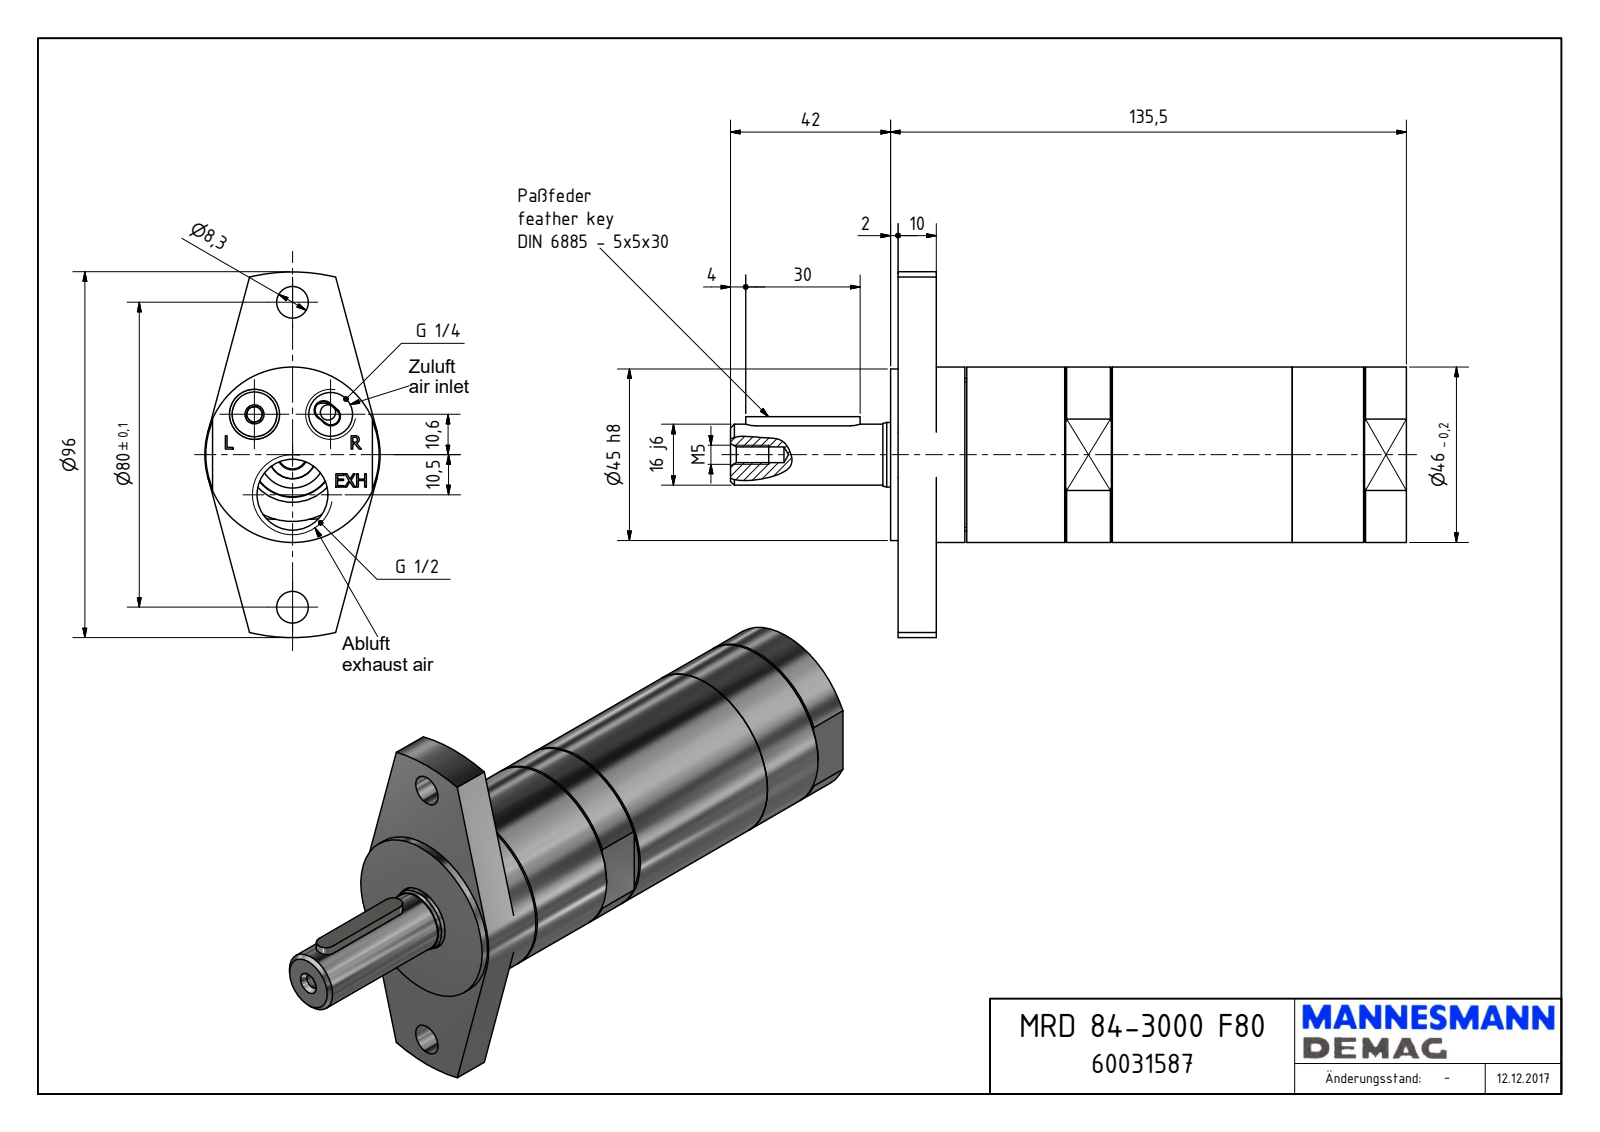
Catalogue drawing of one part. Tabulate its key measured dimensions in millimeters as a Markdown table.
| quantity | value |
| --- | --- |
| part name | MRD 84-3000 F80_60031587 |
| STEP written by | Autodesk Inventor 2018 (AUTOMOTIVE_DESIGN) |
| units | millimeters |
| bodies | 1 solid, 165 faces (108 planar, 31 cylindrical, 26 other) |
| overall size | 177.5 × 96 × 46 |
| volume | 243 723 mm³ |
| surface area | 32 705 mm² |
| round holes (diameter × count) | 8.3 × 2, 4 × 1, 4.13 × 1, 11.45 × 1, 17.5 × 1, 18.63 × 1 |
| round bosses / shafts (diameter × count) | 46 × 1, 45 × 1, 40 × 1, 33.34 × 1, 16.95 × 1, 16 × 1 |
| partial cylindrical surfaces (radius × count) | 2.5 × 2, 5 × 2, 5.72 × 1, 19 × 1, 48 × 1 |
| main face-to-face distances | 10, 2, 12, 123.5, 135.5, 133.5, 42, 8, 115.5, 46 |
| hole center spacings | 14.57, 23.35, 31.05, 40, 51.58, 10.5, 20, 29.5 |
